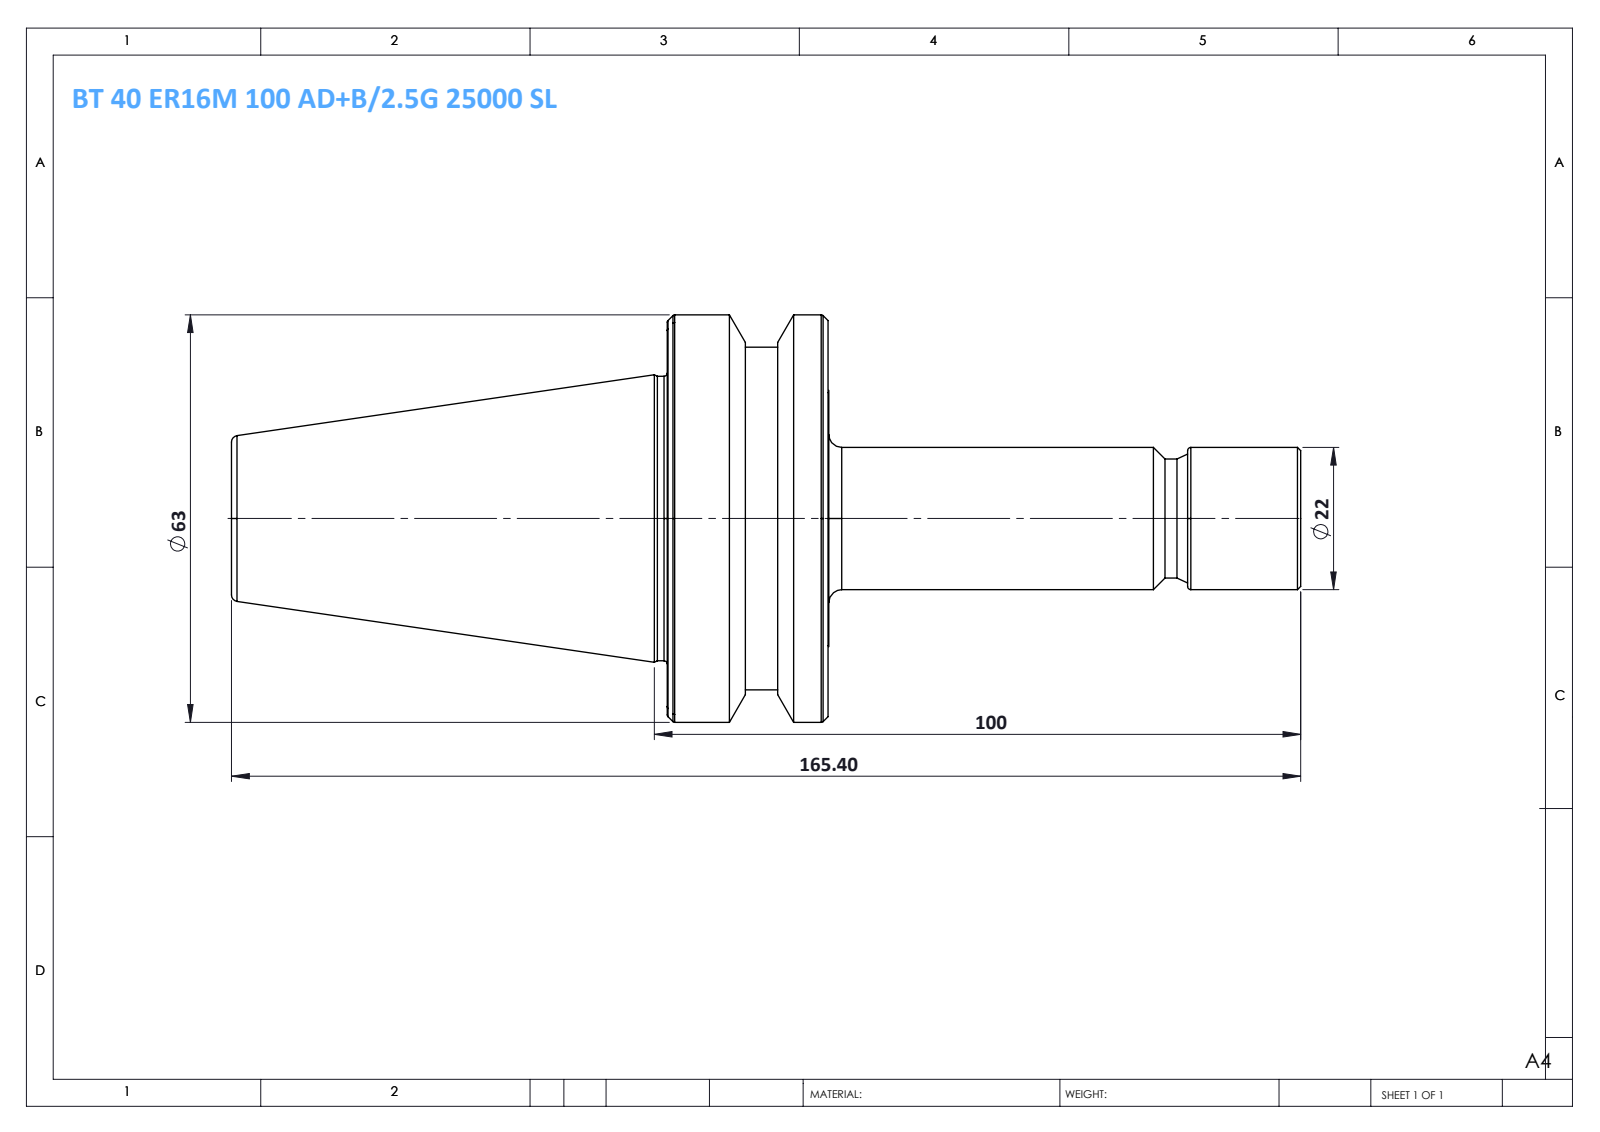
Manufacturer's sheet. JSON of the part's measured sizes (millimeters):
{"part_name": "BT40 ER16M 100 AD+B-2.5G 25000 SL", "step_written_by": "SolidWorks 2014 (CONFIG_CONTROL_DESIGN)", "units": "millimeters", "bodies": {"solids": 1, "faces": 64, "planar": 7, "cylindrical": 14, "other": 43}, "overall_size": [165.4, 63, 63], "volume_mm3": 165730, "surface_area_mm2": 23359, "round_bosses_or_shafts": [[63, 1], [53, 1], [44, 1], [22, 1], [18.4, 1]], "face_to_face_distances": [25, 92.4, 67.4, 73, 98, 165.4, 85.9, 12.9, 12.1, 79.5]}
